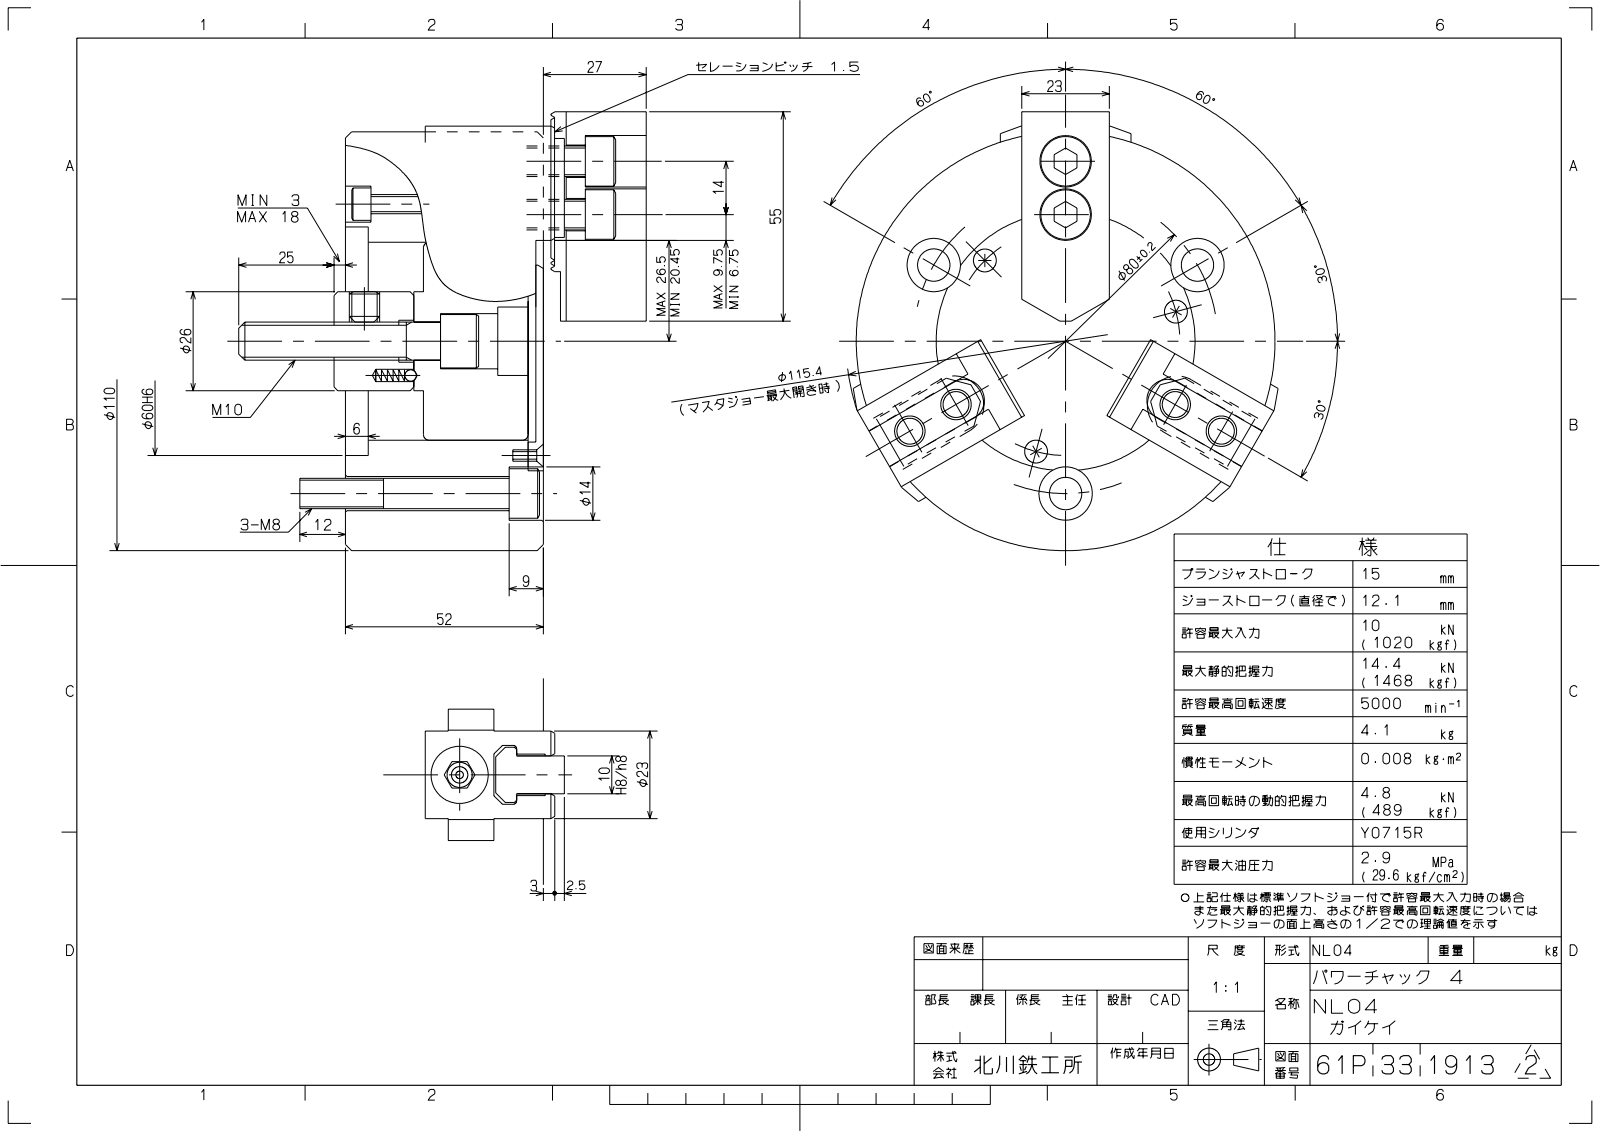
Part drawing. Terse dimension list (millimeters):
name: 61P324176_NL04_ASSY
written by: ST-DEVELOPER v16.7 (AUTOMOTIVE_DESIGN)
unit: mm
bodies: 26 solids, 2033 faces (1771 planar, 162 cylindrical, 100 other)
size: 120.65 × 118.25 × 107.2
volume: 504 376 mm³; area: 143 549 mm²
holes: 9× ⌀8.5, 6× ⌀13.5, 4× ⌀3.2, 3× ⌀2.9, 3× ⌀3.5, 3× ⌀5, 3× ⌀6, 3× ⌀6.3, 3× ⌀9.5, 3× ⌀13, 3× ⌀14, 3× ⌀15
bosses: 6× ⌀13, 6× ⌀8, 3× ⌀8.5, 3× ⌀6, 3× ⌀5, 3× ⌀3, 1× ⌀110, 1× ⌀52
rounds: 6× R1.45, 6× R2.7, 3× R5.5, 3× R7.5, 3× R7.75, 1× R9, 1× R26.5, 1× R34
face distances: 23, 6.5, 6, 21, 13, 52, 12.5, 0.5, 2, 27
hole spacings: 38.16, 38.26, 39.51, 45.99, 64.97, 62.57, 65.18, 75.04
